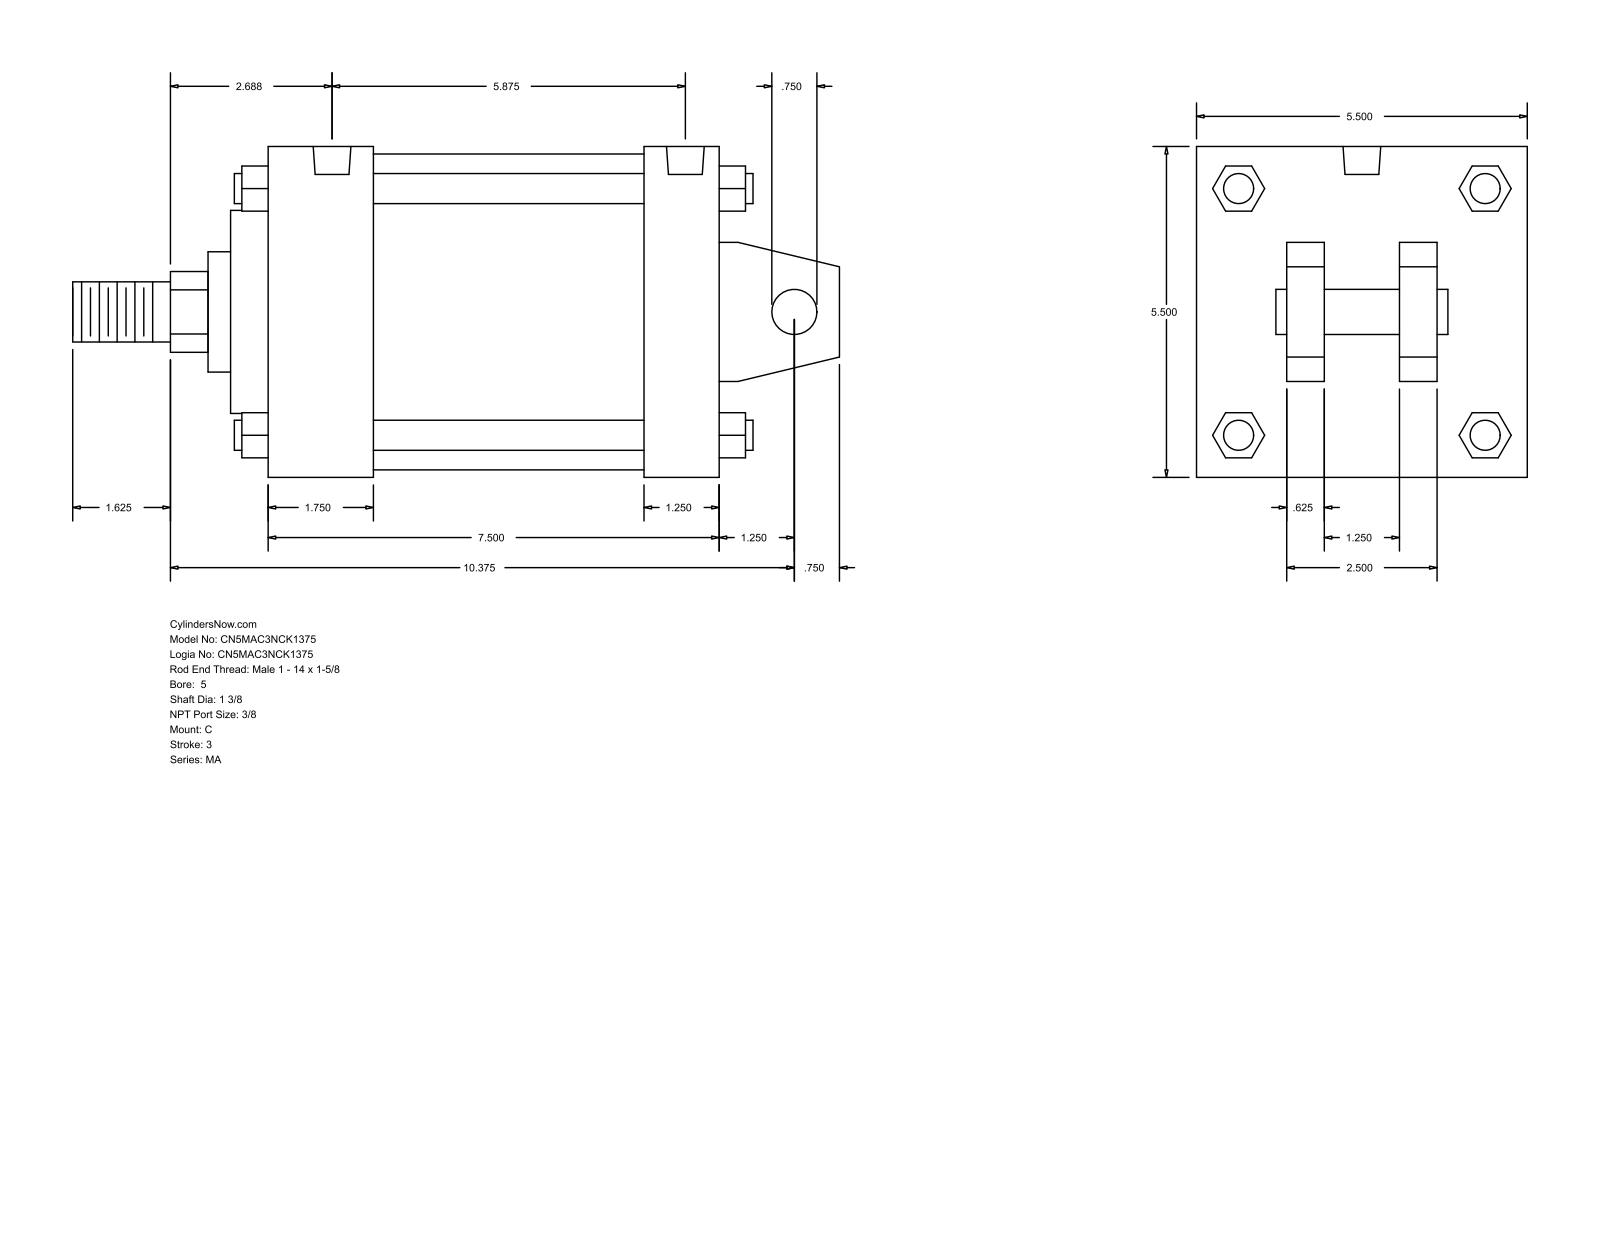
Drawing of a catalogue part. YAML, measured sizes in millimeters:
part_name: "MA_C__0500_1.375"
step_written_by: "GSSL Pune (CONFIG_CONTROL_DESIGN)"
units: millimeters
bodies: {solids: 0, faces: 141, planar: 109, cylindrical: 32, other: 0}
overall_size: [323.85, 139.7, 139.7]
round_holes:
  - {diameter: 11.11, count: 4}
  - {diameter: 15.93, count: 2}
round_bosses_or_shafts:
  - {diameter: 12.7, count: 4}
  - {diameter: 133.35, count: 1}
  - {diameter: 85.72, count: 1}
  - {diameter: 50.8, count: 1}
  - {diameter: 34.92, count: 1}
  - {diameter: 25.4, count: 1}
  - {diameter: 19.05, count: 1}
partial_cylinders:
  - {radius: 17.06, count: 1}
face_to_face_distances: [139.7, 190.51, 15.87, 158.76, 31.75, 44.45, 114.31, 146.06, 53.97, 38.1]
hole_center_spacings: [4.77, 139.69, 144.46, 149.23]
